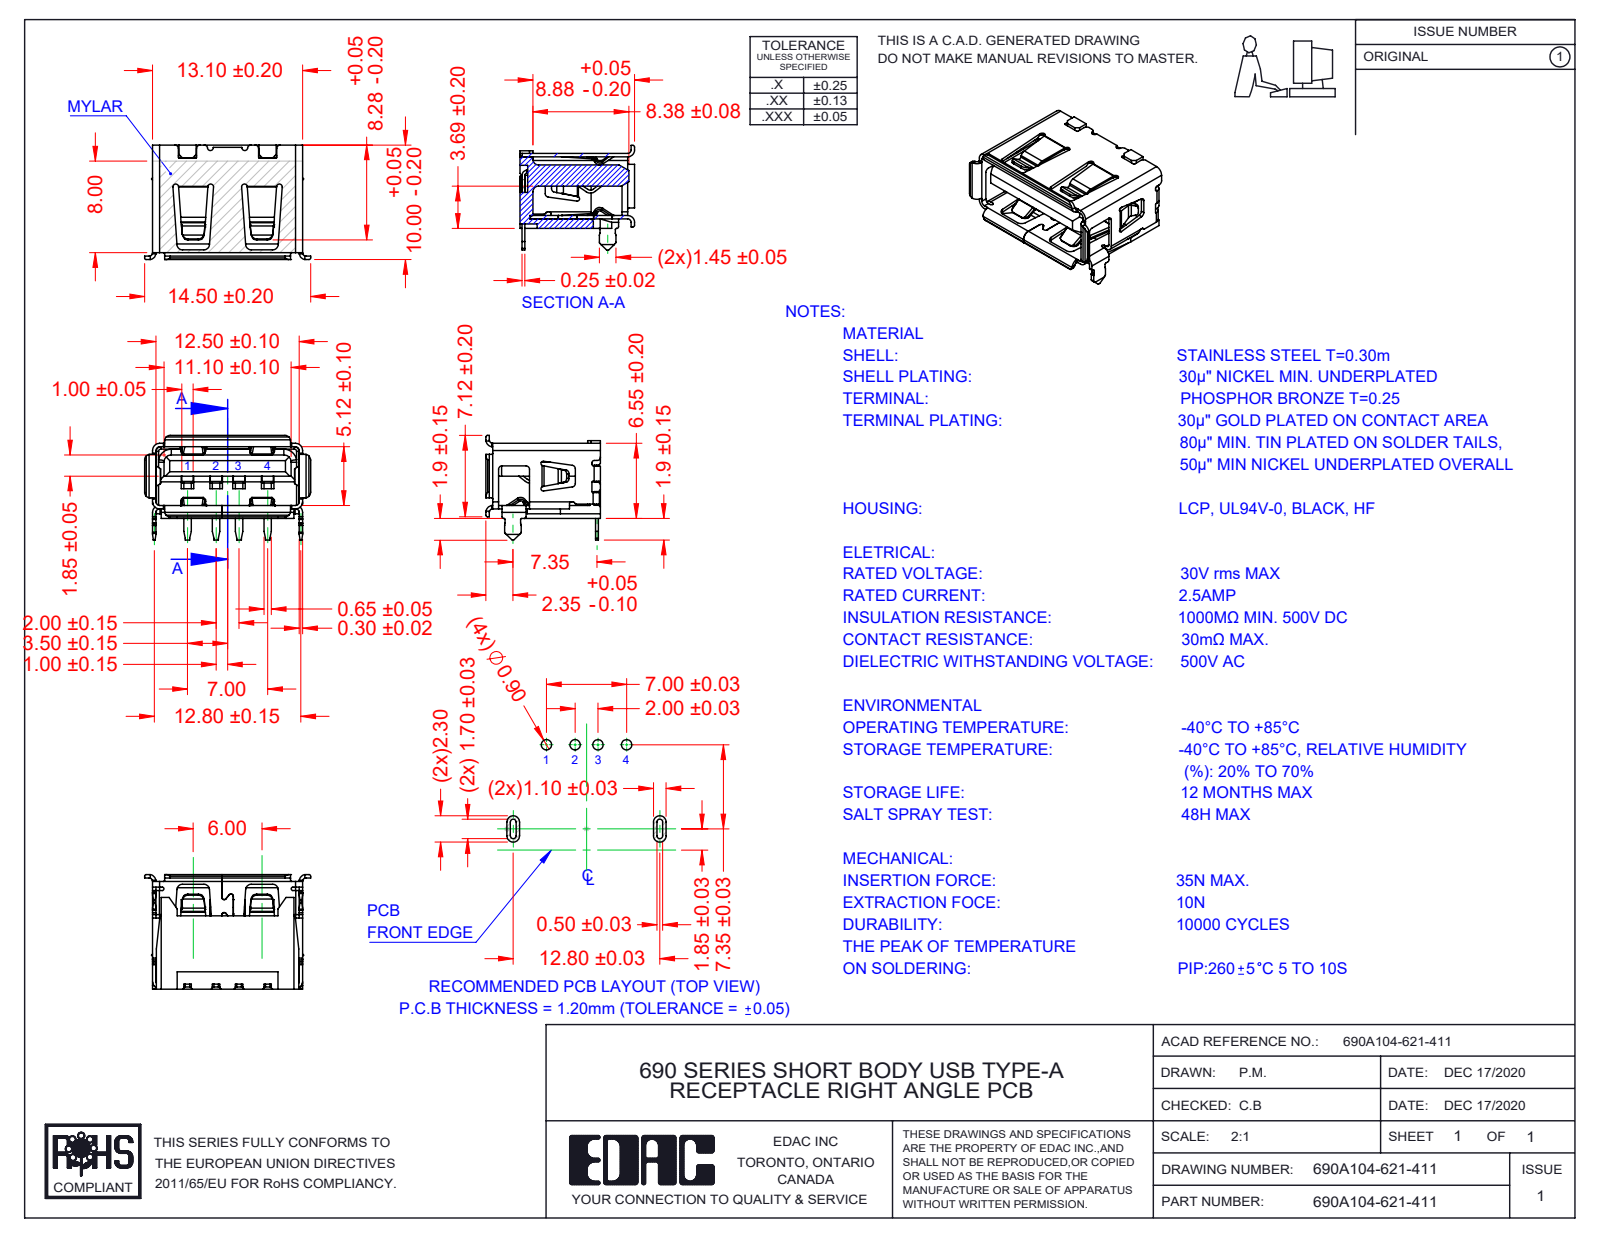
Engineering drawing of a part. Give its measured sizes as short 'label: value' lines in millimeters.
name: Contact 690A104-621-411; Insulator 690A104-621-411; Shell 690A104-621-411; 690A104-621-411
written by: SolidWorks 2020 (AUTOMOTIVE_DESIGN)
unit: mm
bodies: 6 solids, 1256 faces (712 planar, 391 cylindrical, 153 other)
size: 14.5 × 10 × 9.15
volume: 328 mm³; area: 1 499 mm²
rounds: 48× R0.13, 40× R0.3, 36× R0.1, 33× R0.2, 30× R0.5, 28× R0.15, 10× R0.6, 9× R0.25
face distances: 5.42, 2.86, 2.56, 0.45, 5.72, 1.4, 0.71, 6.25, 2.5, 4.71
